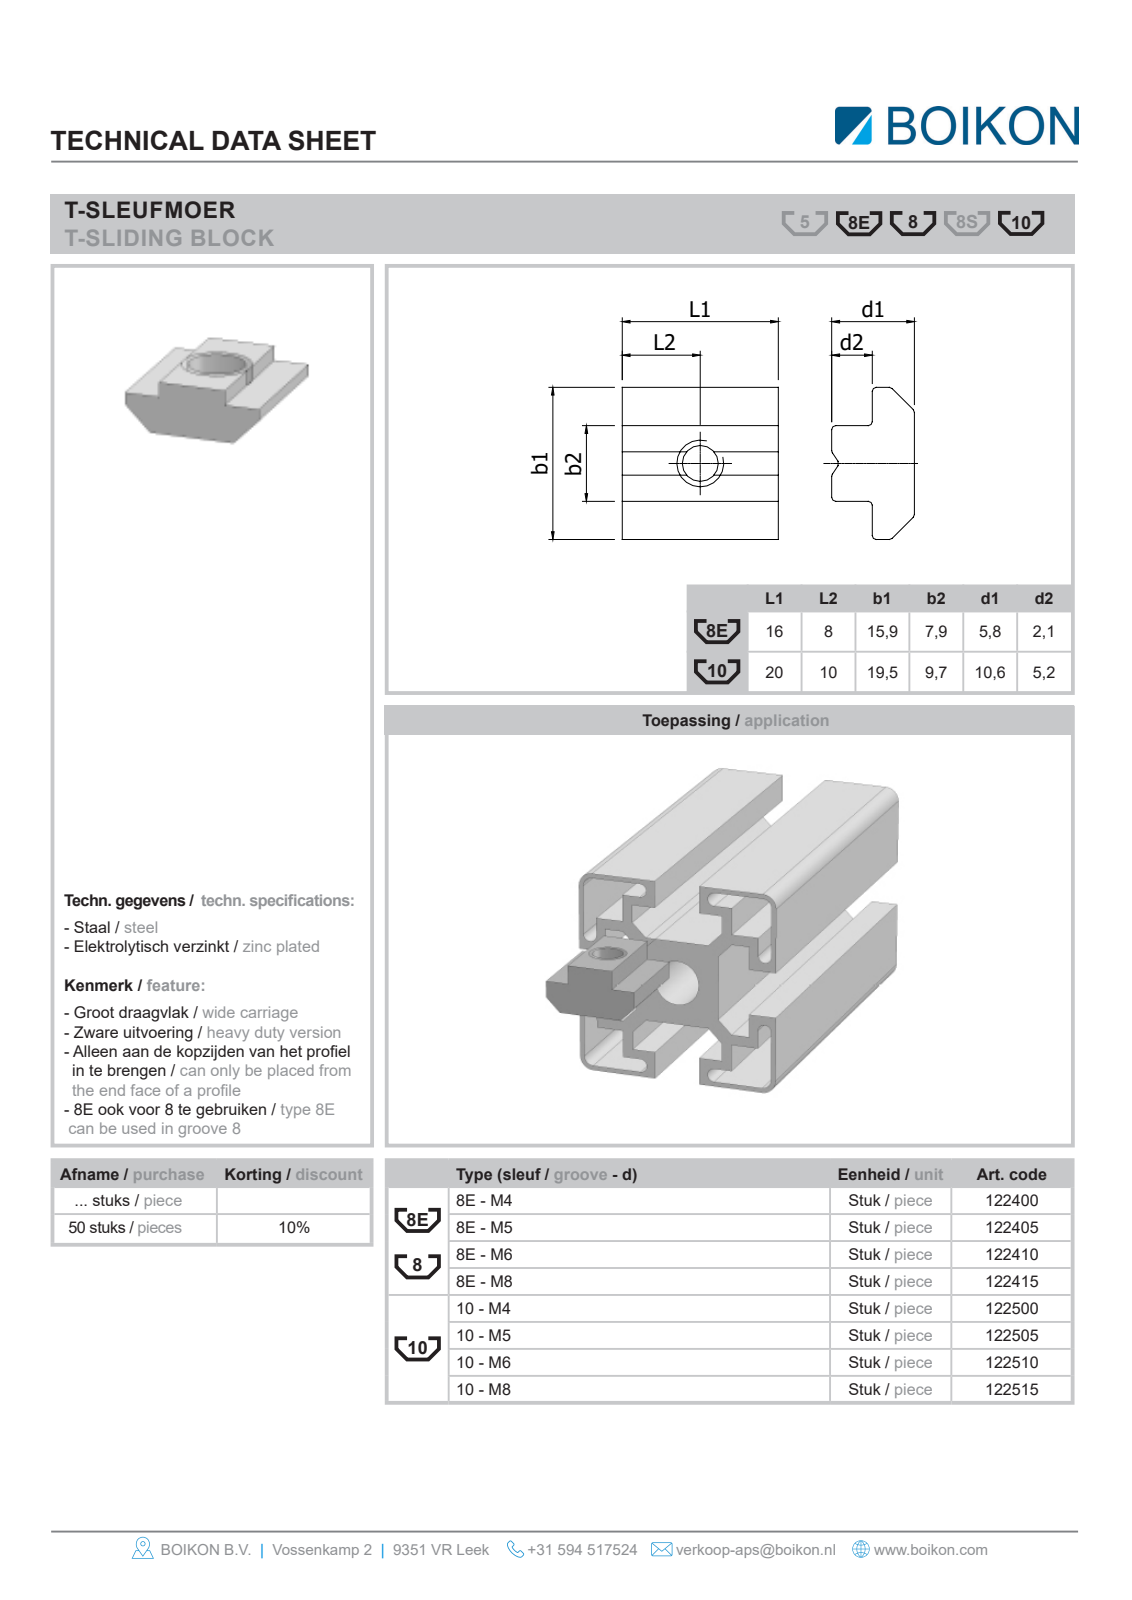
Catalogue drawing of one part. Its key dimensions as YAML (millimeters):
part_name: "Root; 122500T-Sleufmoer 10 - M4BOIKON"
step_written_by: "HiCAD 2013 1802.4 Build 509 (AUTOMOTIVE_DESIGN)"
units: millimeters
bodies: {solids: 1, faces: 13, planar: 12, cylindrical: 1, other: 0}
overall_size: [20, 19.5, 11.3]
volume: 2999
surface_area: 1550
round_holes:
  - {diameter: 4, count: 1}
face_to_face_distances: [6.5, 10.5, 4, 20, 4.9, 14.6, 9.7, 19.5]
